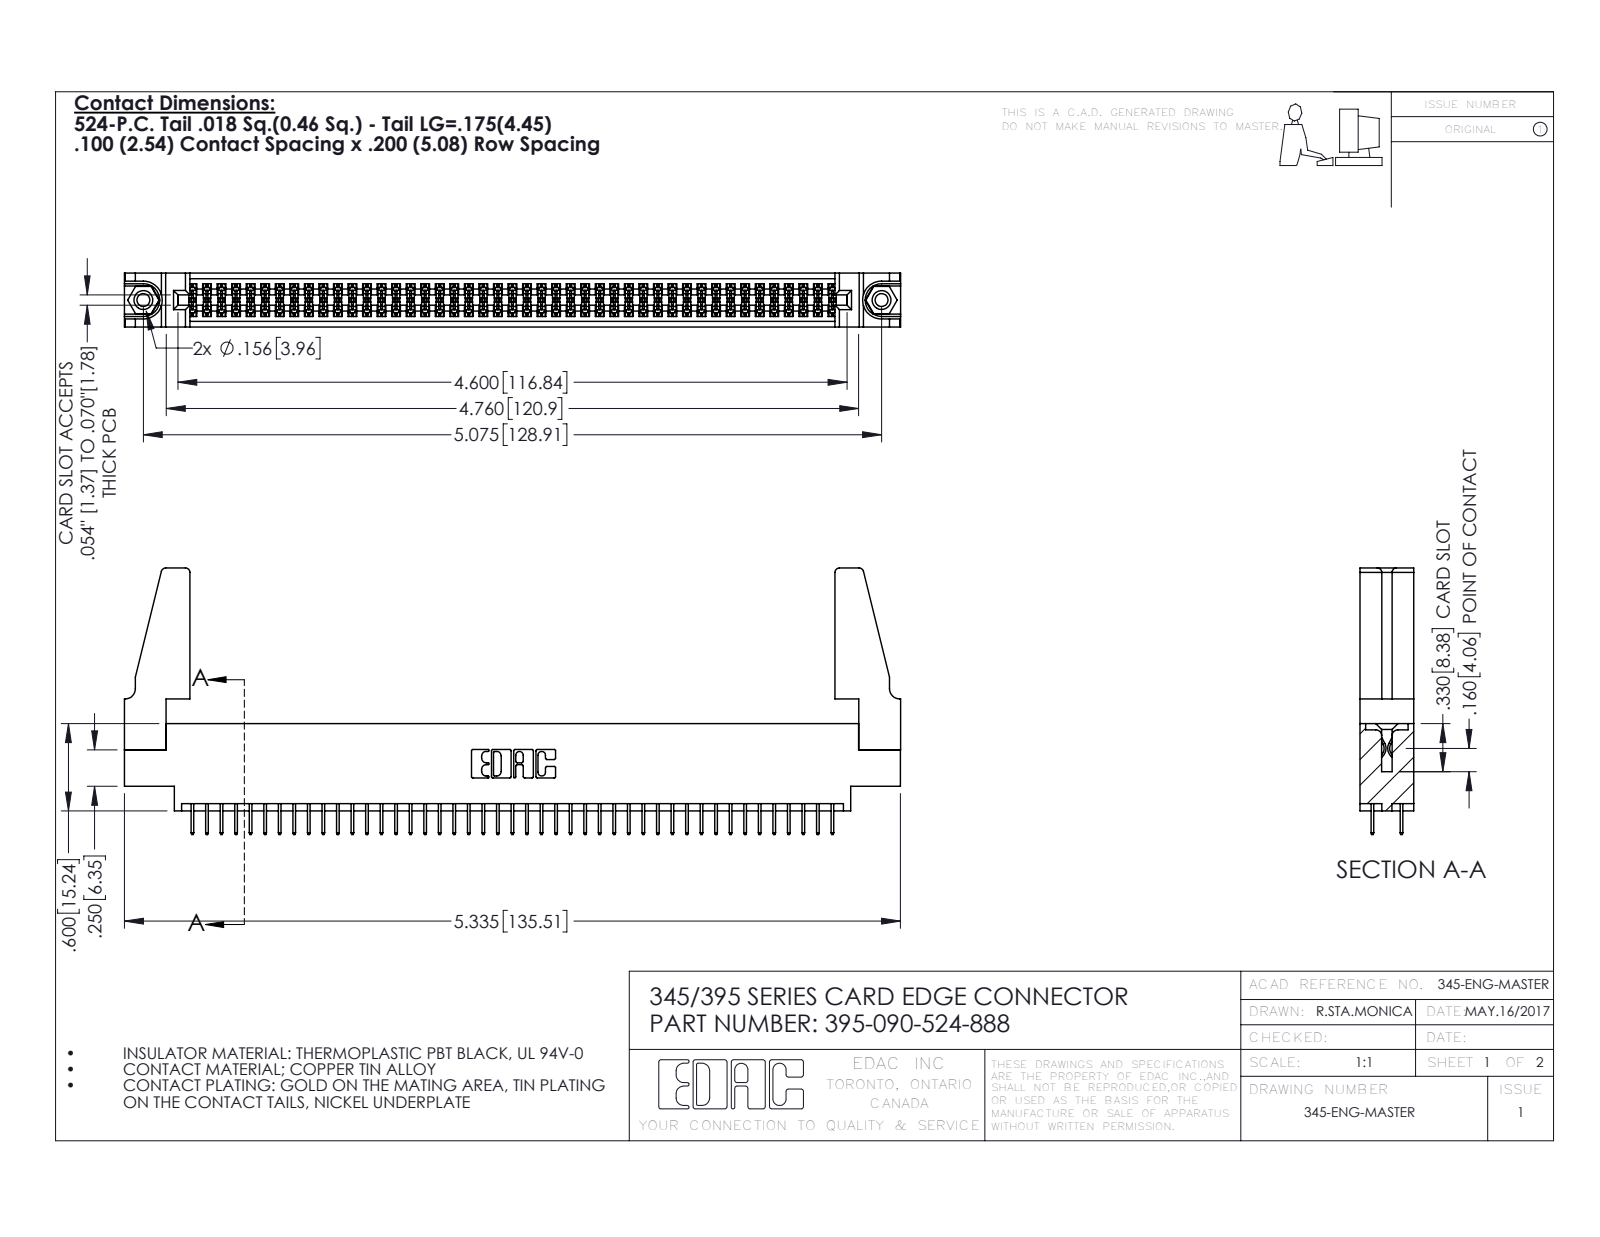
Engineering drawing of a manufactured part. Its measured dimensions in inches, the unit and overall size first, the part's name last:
Units: inches
Overall size (bounding box): 5.336 × 1.832 × 0.37
Round holes (diameter × count): ⌀0.089 ×2, ⌀0.125 ×2, ⌀0.156 ×2, ⌀0.064 ×1
Round bosses / shafts (diameter × count): ⌀0.155 ×2
Partial cylindrical surfaces — rounded edges, fillets, slot ends (radius × count): R0.006 ×135, R0.01 ×22, R0.03 ×8, R0.007 ×6, R0.031 ×6, R0.026 ×3, R0.014 ×2, R0.019 ×2
Main face-to-face distances: 0.072, 0.298, 0.37, 0.2, 0.098, 0.272, 0.025, 0.225, 0.175, 0.072
Hole centre spacings: 0.27, 4.839, 5.075
Volume: 0.988 in³ · Surface area: 34.25 in²
Bodies: 95 solids, 5114 faces (3666 planar, 1432 cylindrical, 16 other)
Part name (STEP PRODUCT): 345-220-078_345-220-088; 395-090-524-888; 345-292-001_345-293-124; 345 Part_0.170 Offset - 0.156 Dia-TH (+1 more)
STEP written by: SolidWorks 2016 (CONFIG_CONTROL_DESIGN)
